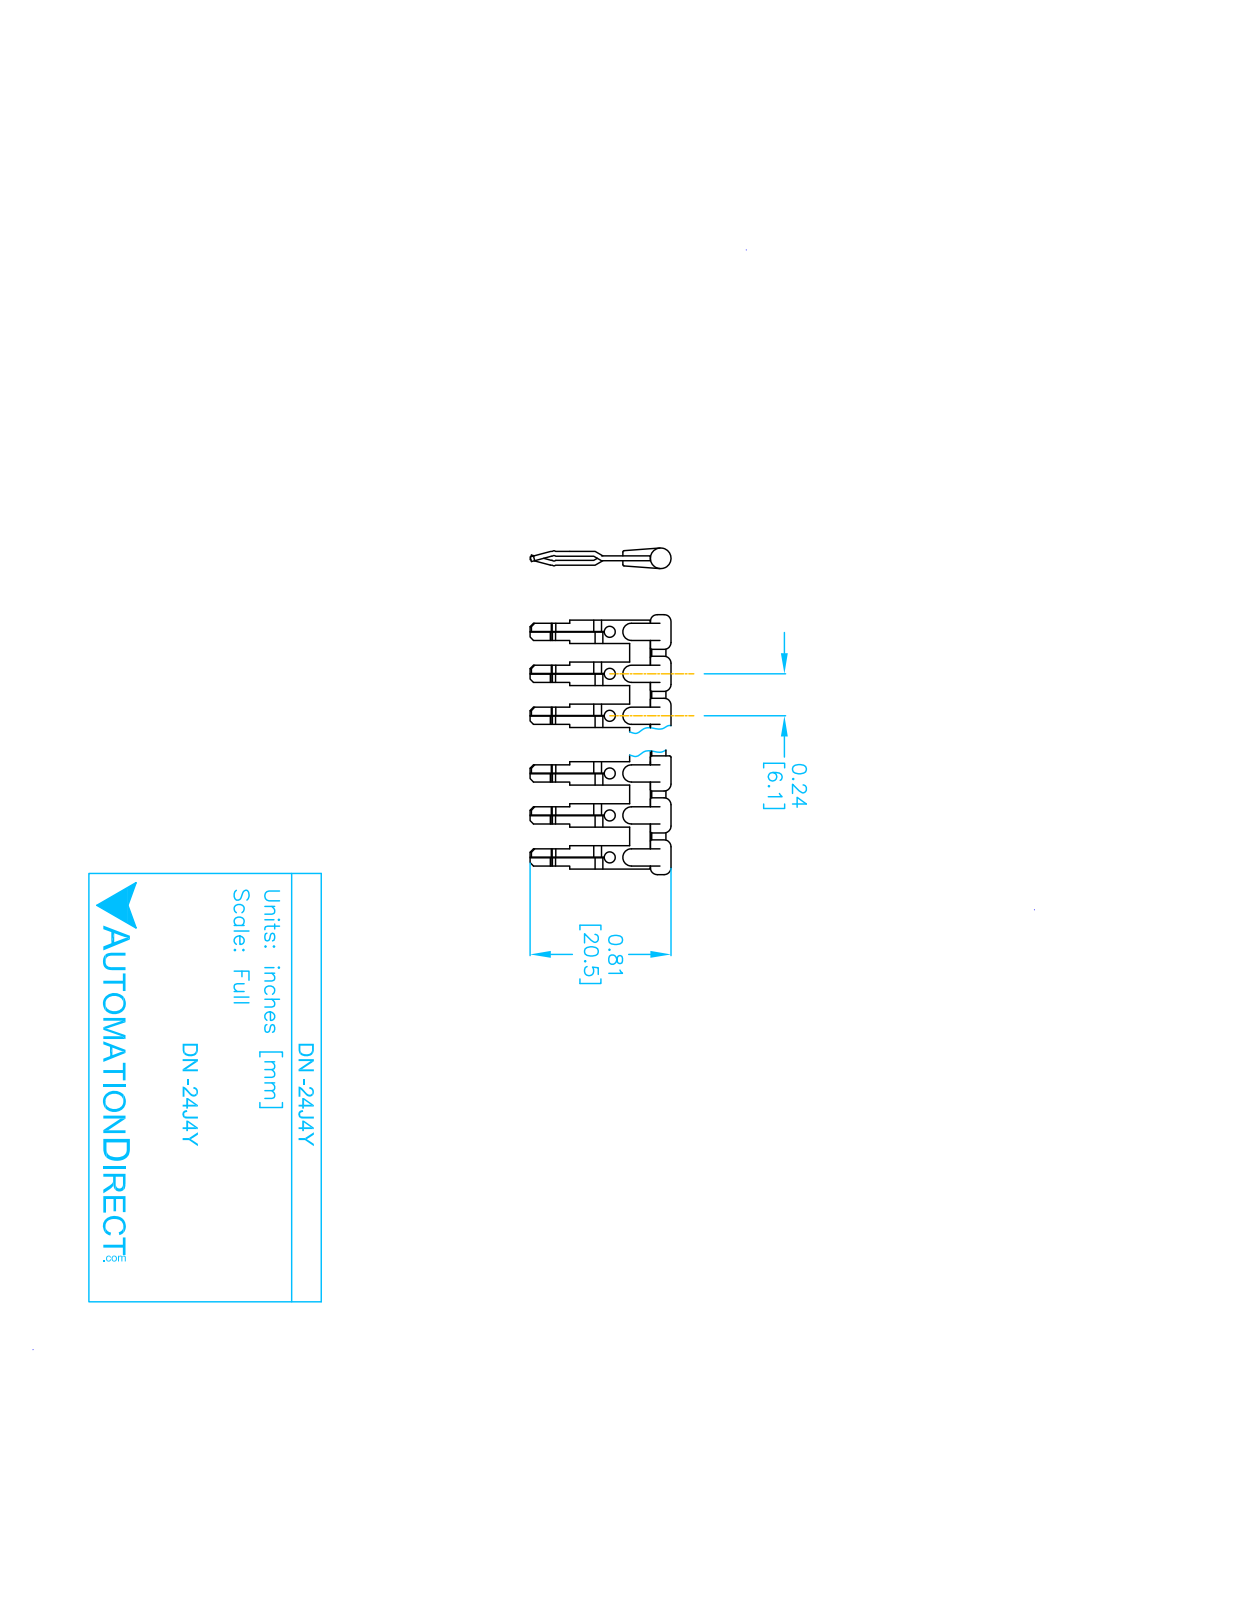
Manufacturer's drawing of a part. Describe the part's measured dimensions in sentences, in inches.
The part is named "J4_M; J4_N; J4PSX_J4 INTERMEDIO; 43520_24_DN-24J4Y (+1 more)". Its 3-D file was written by "SolidWorks 2013 (AUTOMOTIVE_DESIGN)". It is 50 solids with 1905 faces: 1113 planar, 567 cylindrical and 225 other. Overall it measures 5.742 by 0.801 by 0.118 inches. Its volume is 0.157 cubic inches and its surface area 10.58 square inches. Round holes: 48 of diameter 0.051. Round bosses or shafts: 1 of diameter 0.118. Partial cylindrical surfaces (rounded edges, fillets, slot ends): 100 of radius 0.02, 25 of radius 0.049, 4 of radius 0.028, 1 of radius 0.03. The main face-to-face distances are 0.028, 0.022, 0.049, 0.043, 0.071, 0.016, 0.24, 0.48, 0.72, 0.028. The hole center spacings are 0.24, 0.29, 0.48, 0.507, 0.72, 0.739, 0.961, 0.974.
